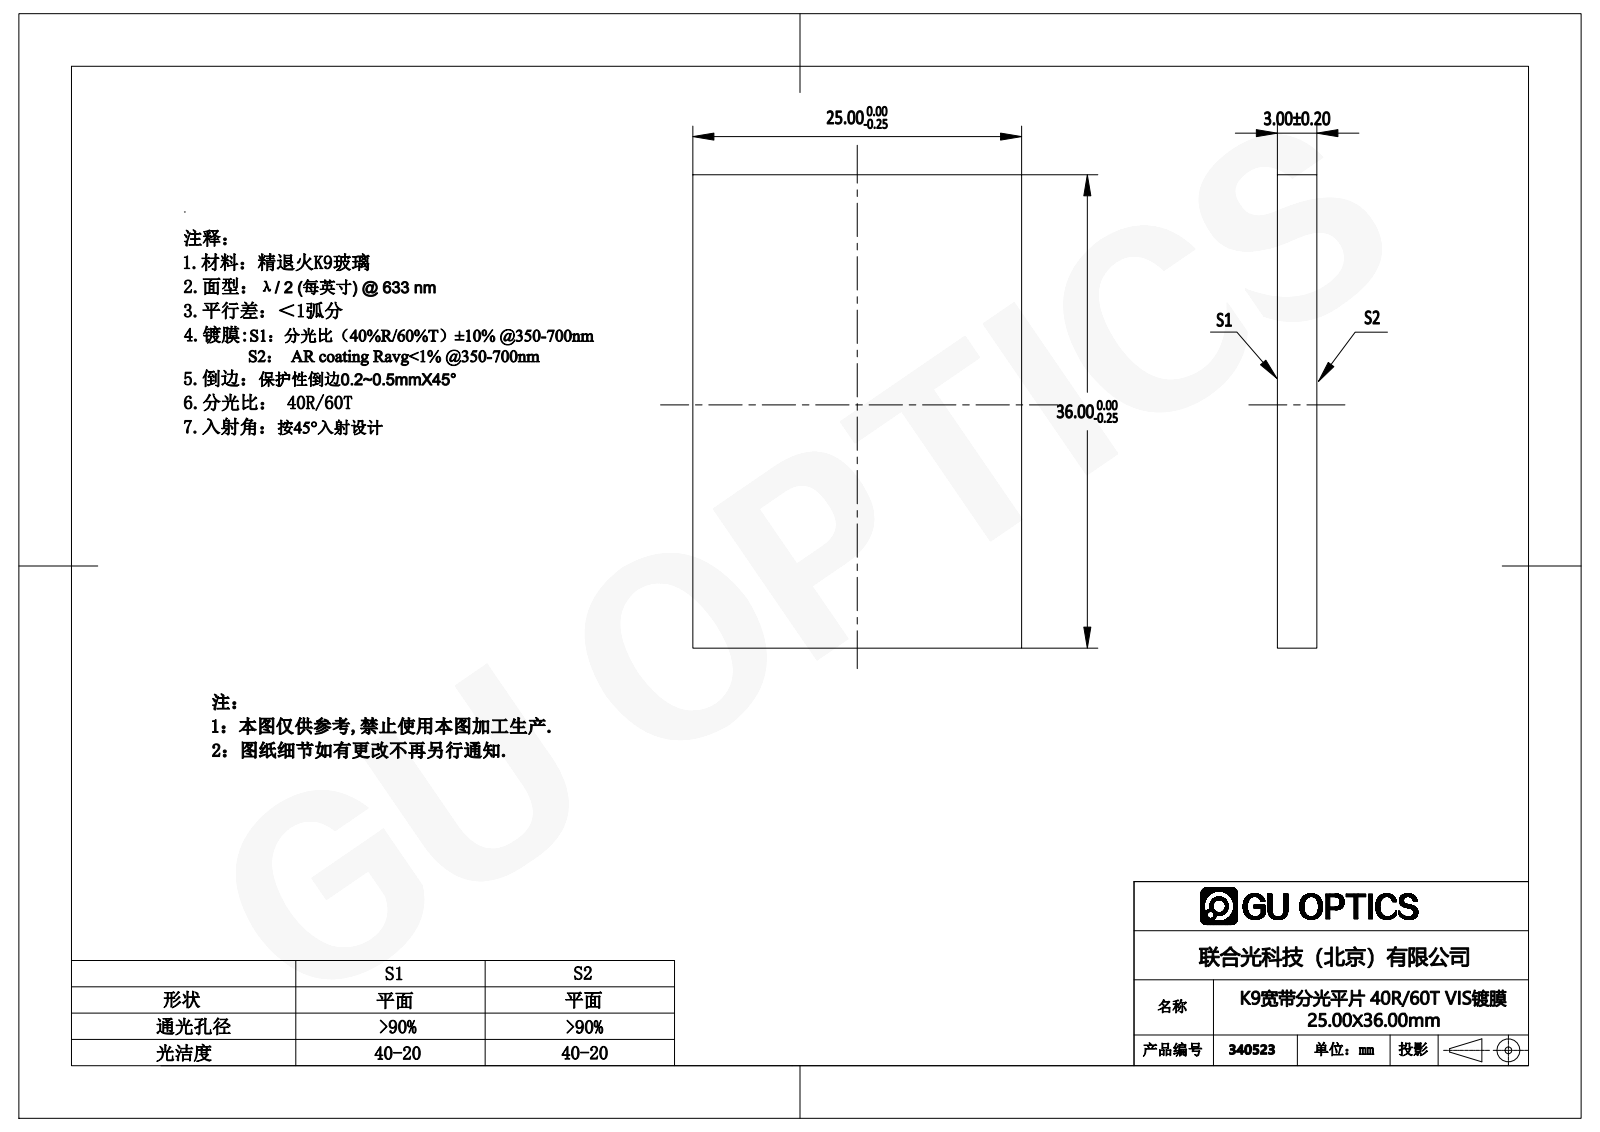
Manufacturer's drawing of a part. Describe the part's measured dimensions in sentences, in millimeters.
The part is named "340523". Its 3-D file was written by "SolidWorks 2016 (CONFIG_CONTROL_DESIGN)". It is 1 solid with 6 faces: 6 planar, 0 cylindrical and 0 other. Overall it measures 36 by 25 by 3 millimeters. Its volume is 2 700 cubic millimeters and its surface area 2 166 square millimeters. The main face-to-face distances are 3, 25, 36.
